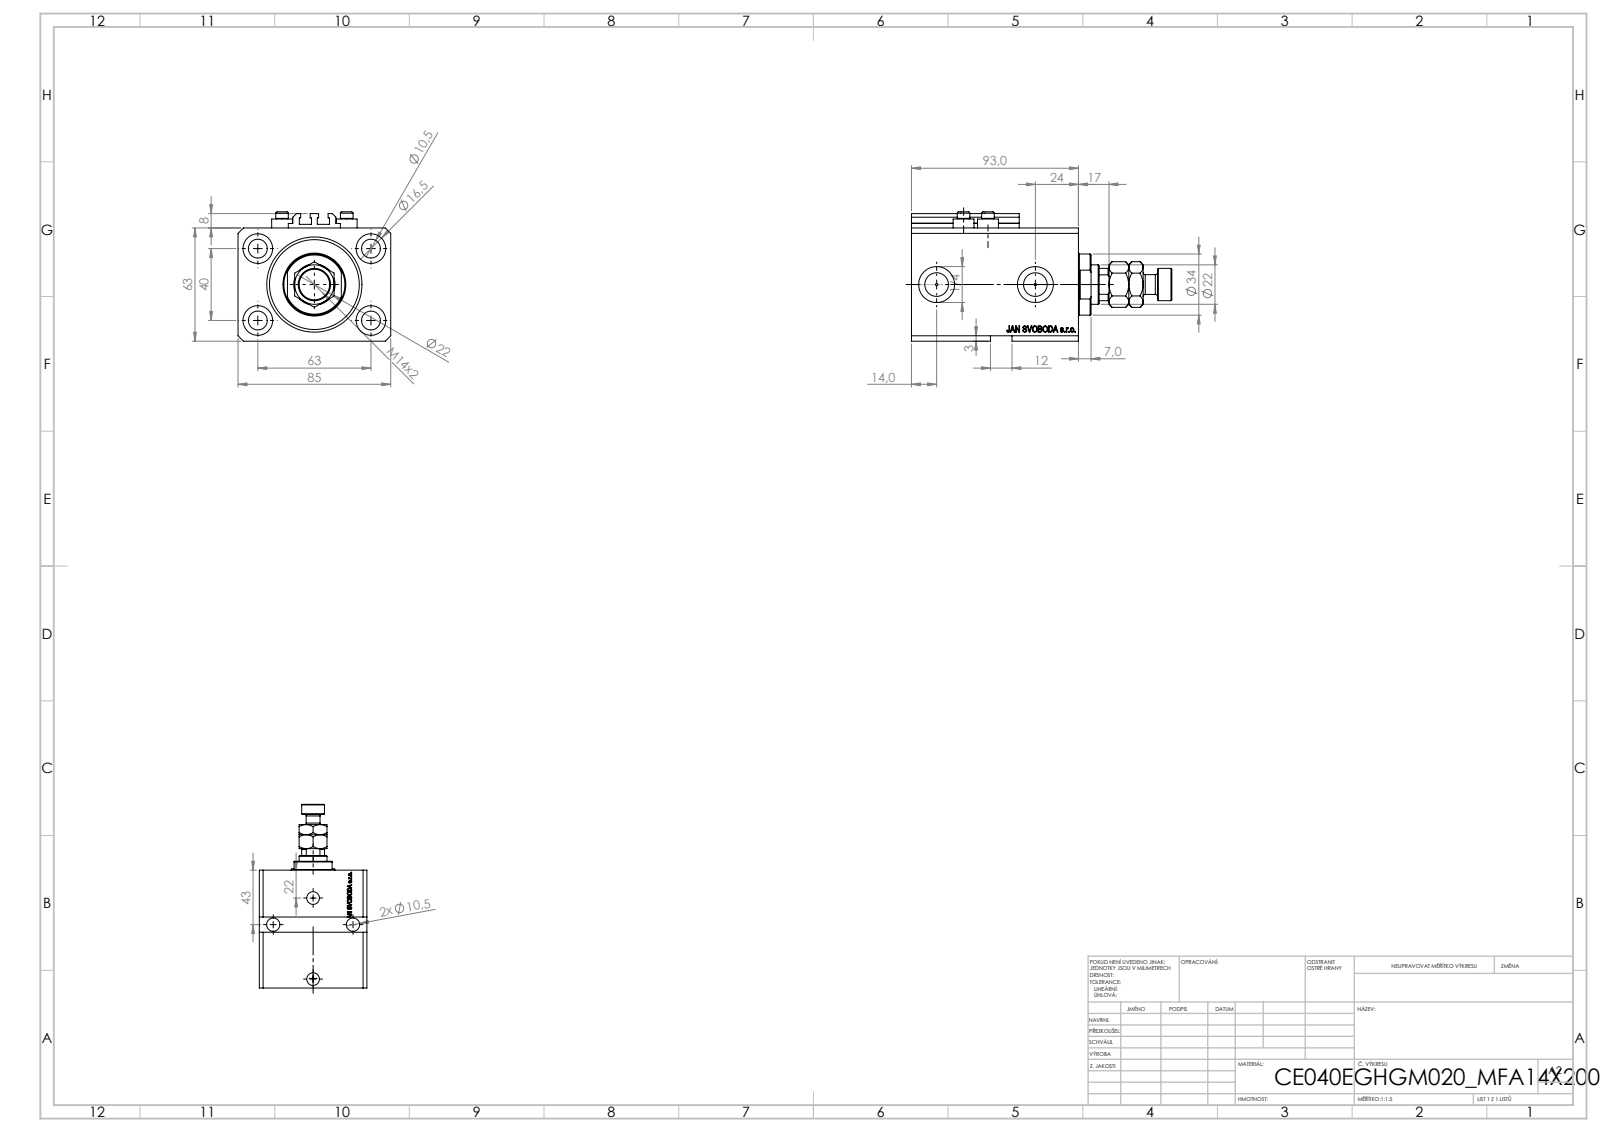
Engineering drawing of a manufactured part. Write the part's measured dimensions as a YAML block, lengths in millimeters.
part_name: "V250CE_E_Body; V250CE_VC_E; V250CE_C_VCP; MFA (+1 more)"
step_written_by: "SolidWorks 2019 (CONFIG_CONTROL_DESIGN)"
units: millimeters
bodies: {solids: 9, faces: 1139, planar: 551, cylindrical: 130, other: 458}
overall_size: [144.9, 85, 72]
volume: 447919
surface_area: 101180
round_holes:
  - {diameter: 10.5, count: 6}
  - {diameter: 1.25, count: 4}
  - {diameter: 4, count: 4}
  - {diameter: 16.5, count: 4}
  - {diameter: 10, count: 2}
  - {diameter: 13.16, count: 2}
  - {diameter: 20, count: 2}
  - {diameter: 12.5, count: 1}
  - {diameter: 22, count: 1}
  - {diameter: 40, count: 1}
  - {diameter: 53, count: 1}
round_bosses_or_shafts:
  - {diameter: 11.6, count: 4}
  - {diameter: 7, count: 4}
  - {diameter: 34, count: 1}
  - {diameter: 18, count: 1}
  - {diameter: 11, count: 1}
partial_cylinders:
  - {radius: 0.2, count: 10}
  - {radius: 10.5, count: 1}
face_to_face_distances: [63, 85, 93, 65.9, 54.5, 27.1, 11.4, 81.6, 3, 65]
hole_center_spacings: [37.31, 63, 13.6, 15.4, 24.96, 28.02, 28.43, 33.62]
